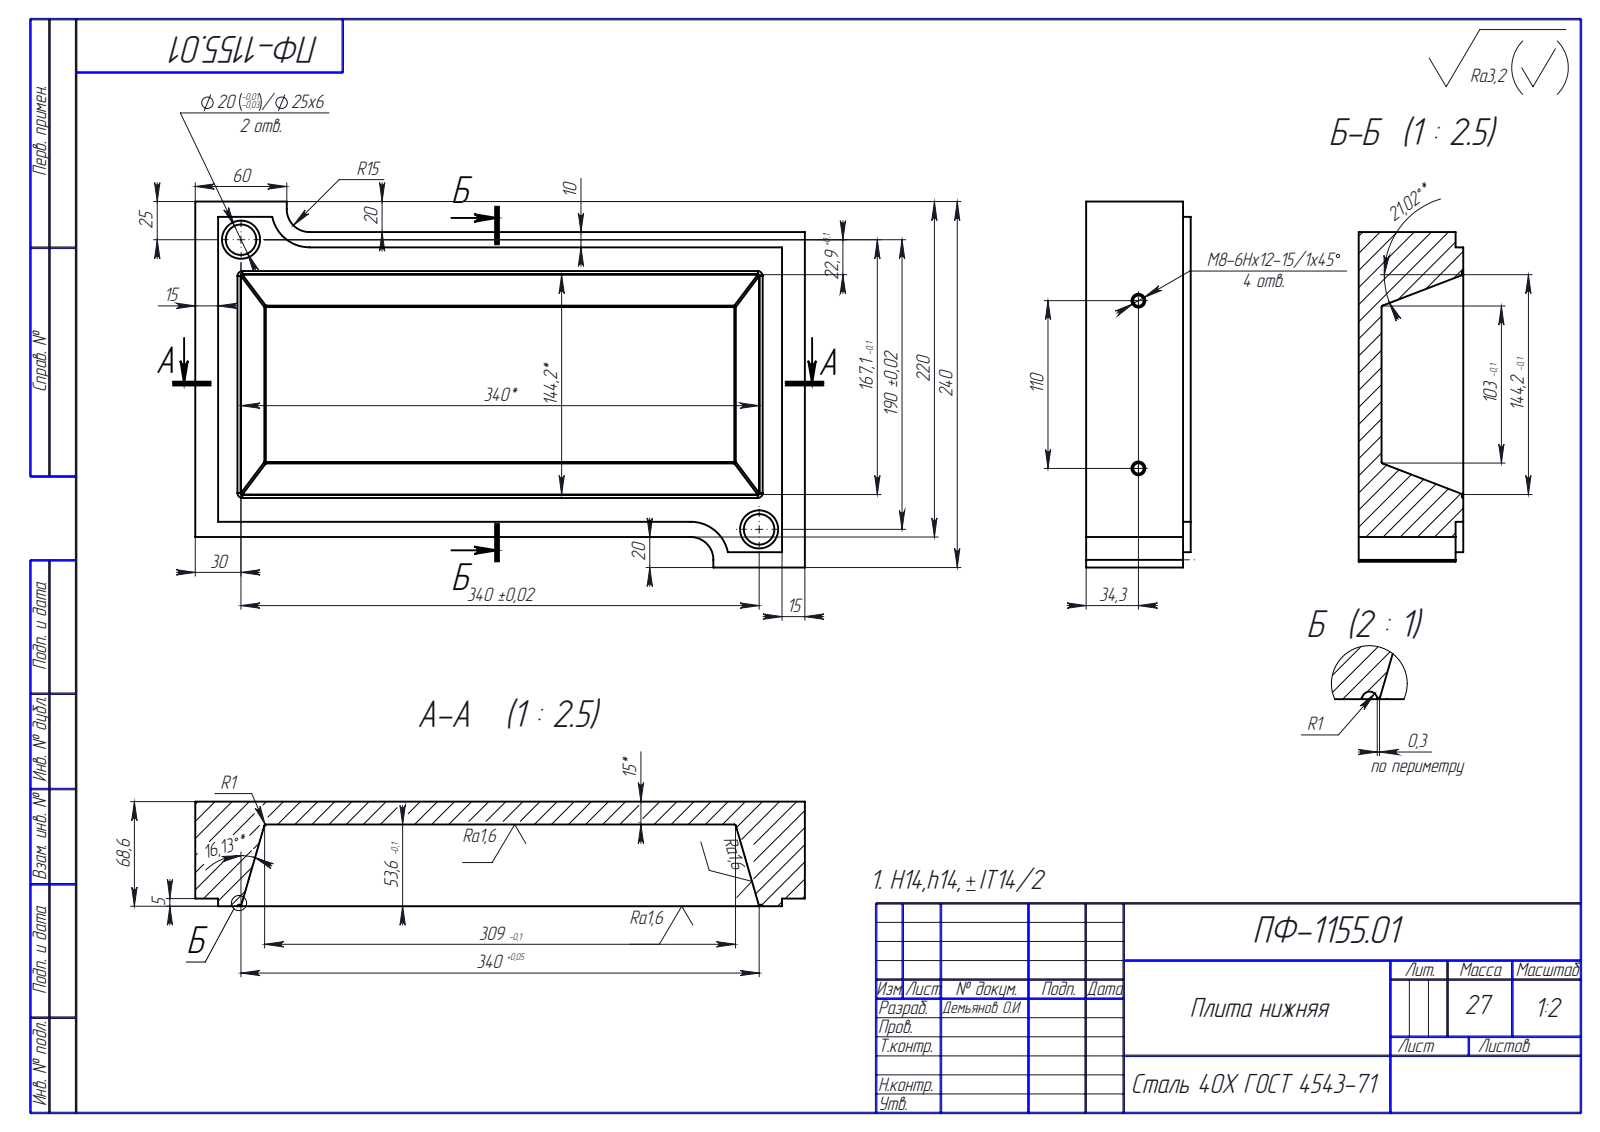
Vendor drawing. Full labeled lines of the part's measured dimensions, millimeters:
Part name (STEP PRODUCT): НЛС-ПФ-1155-01 Плита нижняя
STEP written by: SolidWorks 2012 (AUTOMOTIVE_DESIGN)
Units: millimetres
Bodies: 1 solid, 87 faces (25 planar, 34 cylindrical, 28 other)
Overall size (bounding box): 400 × 240 × 68.6
Volume: 3 383 000 mm³ · Surface area: 295 252 mm²
Round holes (diameter × count): ⌀6.8 ×2, ⌀20 ×2, ⌀25 ×2
Partial cylindrical surfaces — rounded edges, fillets, slot ends (radius × count): R1 ×12, R15 ×2, R25 ×2
Main face-to-face distances: 15, 200, 68.6, 53.6, 63.6, 48.6, 5, 400, 20, 220
Hole centre spacings: 110, 389.49
